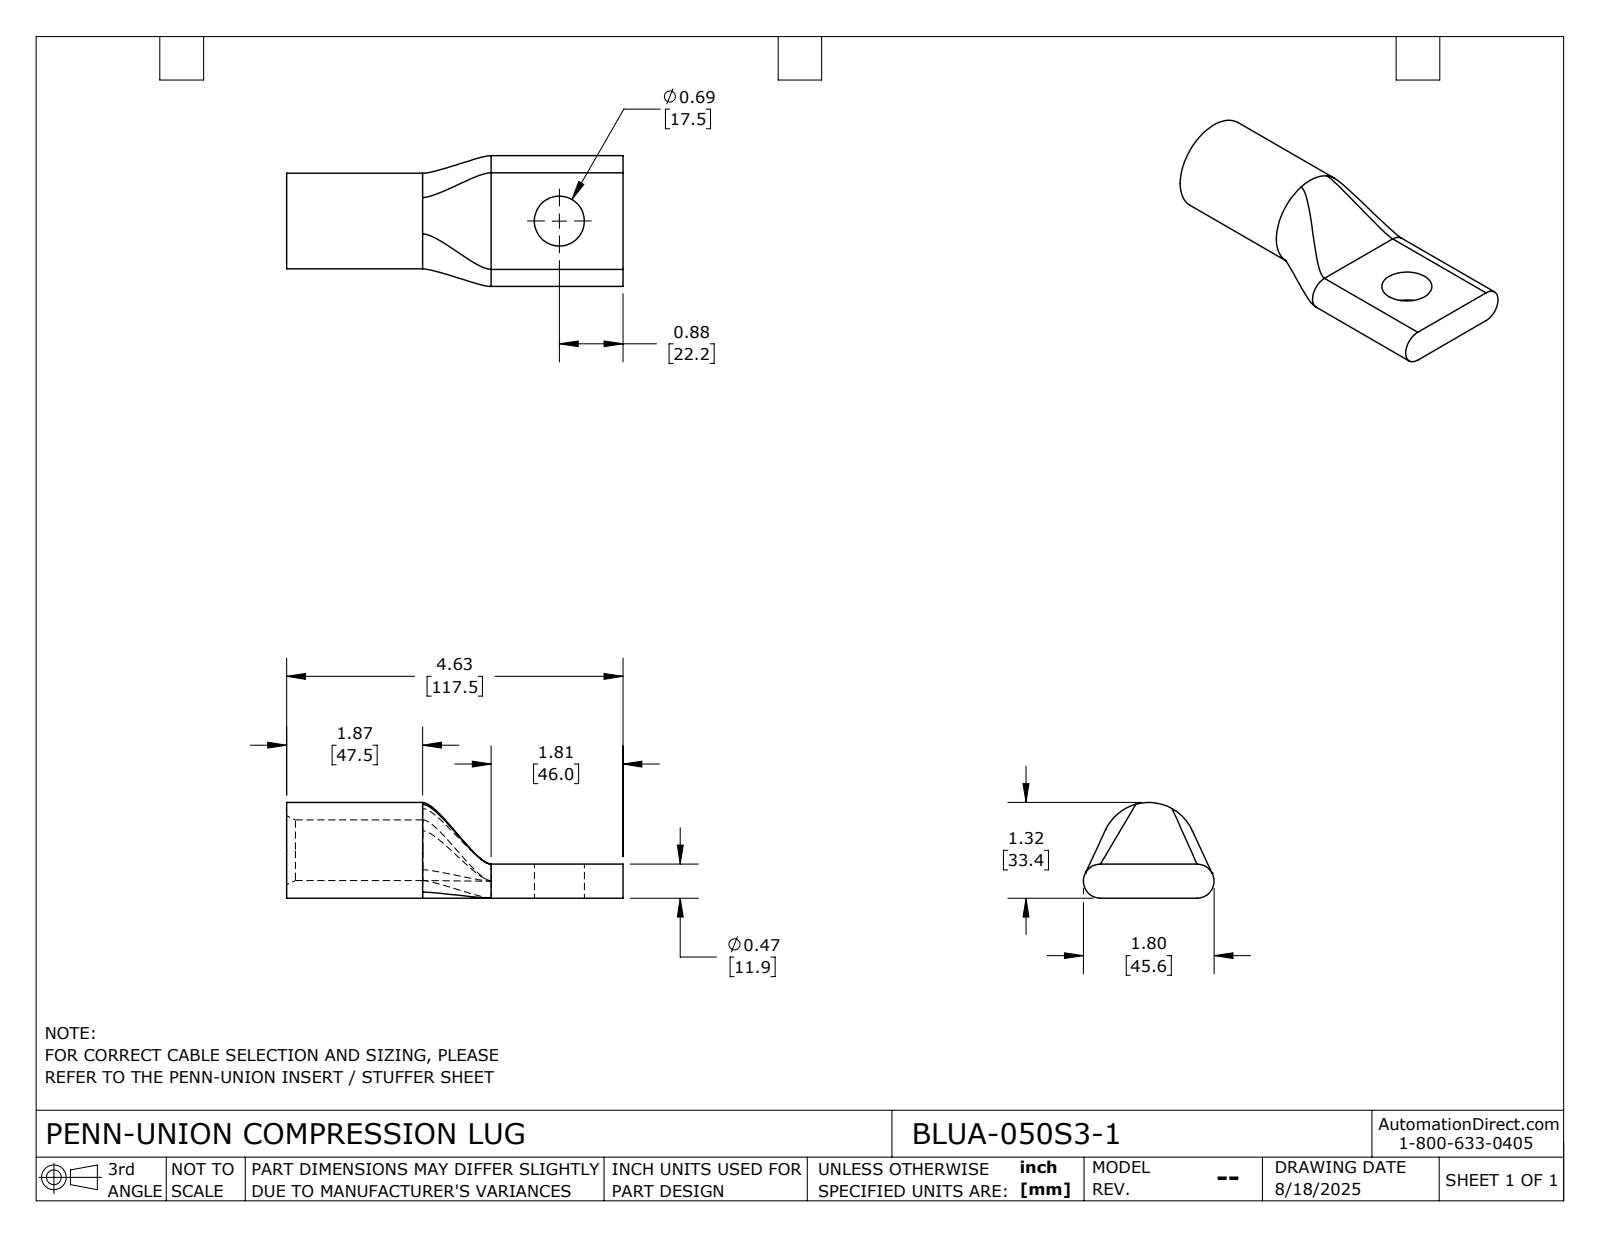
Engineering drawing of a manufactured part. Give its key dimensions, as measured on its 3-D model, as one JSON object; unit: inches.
{"part_name": "BLUA-050S3-1", "step_written_by": "SolidWorks 2024 (CONFIG_CONTROL_DESIGN)", "units": "inches", "bodies": {"solids": 1, "faces": 24, "planar": 5, "cylindrical": 9, "other": 10}, "overall_size": [4.625, 1.797, 1.315], "volume_in3": 3.528, "surface_area_in2": 28.94, "round_holes": [[0.687, 1], [0.834, 1]], "round_bosses_or_shafts": [[1.315, 1]], "partial_cylinders_radius": [[0.234, 2]], "face_to_face_distances": [0.469, 4.625, 2.813, 1.812]}
